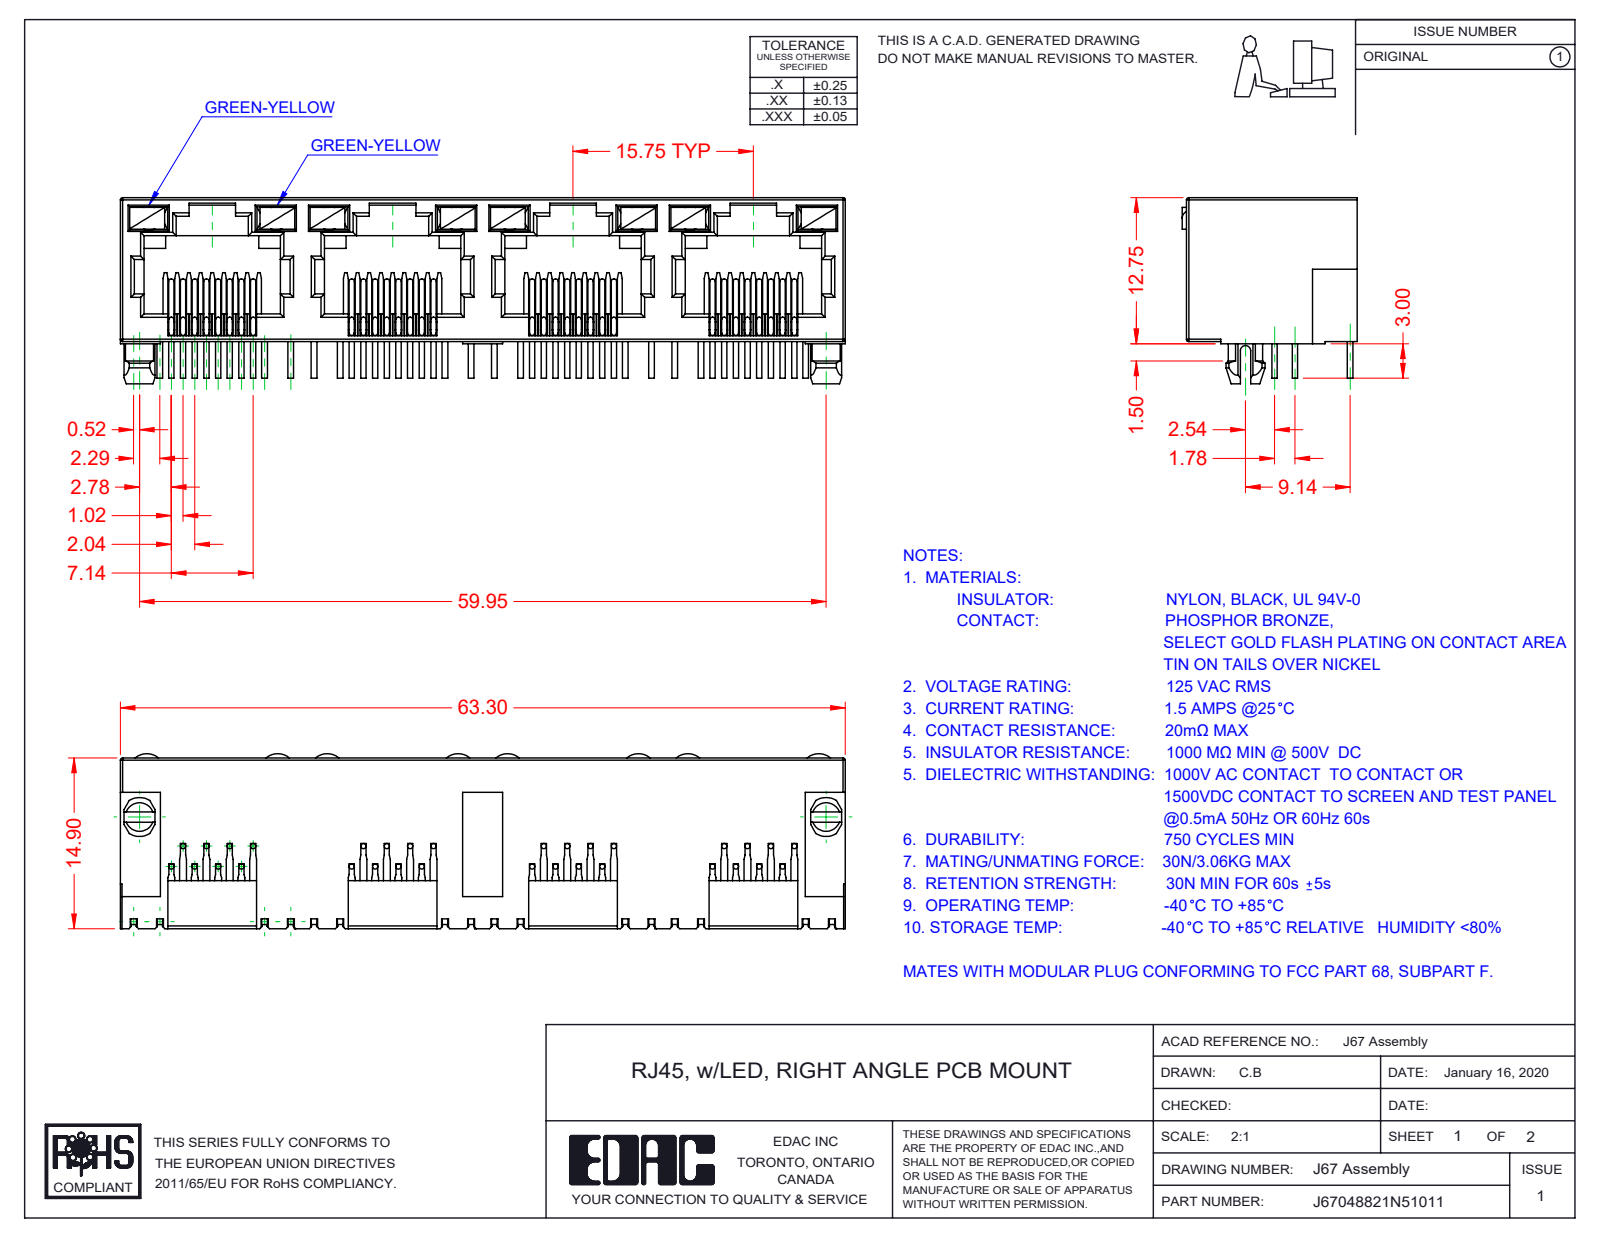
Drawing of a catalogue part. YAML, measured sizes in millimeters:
part_name: "J67048822N55011; 67 Contacts; 67 LED RH_5-Green-Yellow; 67 Insulator (+1 more)"
step_written_by: "SolidWorks 2016 (CONFIG_CONTROL_DESIGN)"
units: millimeters
bodies: {solids: 41, faces: 2481, planar: 1781, cylindrical: 492, other: 208}
overall_size: [63.3, 16.25, 15.28]
volume: 5159
surface_area: 11573
round_bosses_or_shafts:
  - {diameter: 0.46, count: 96}
partial_cylinders:
  - {radius: 0.2, count: 66}
  - {radius: 0.3, count: 29}
  - {radius: 0.45, count: 9}
  - {radius: 1.55, count: 8}
  - {radius: 1.5, count: 2}
  - {radius: 1.7, count: 2}
  - {radius: 0.35, count: 1}
  - {radius: 1, count: 1}
face_to_face_distances: [0.5, 12.55, 1.89, 0.89, 10, 15.75, 1, 1.39, 11, 11.89]
